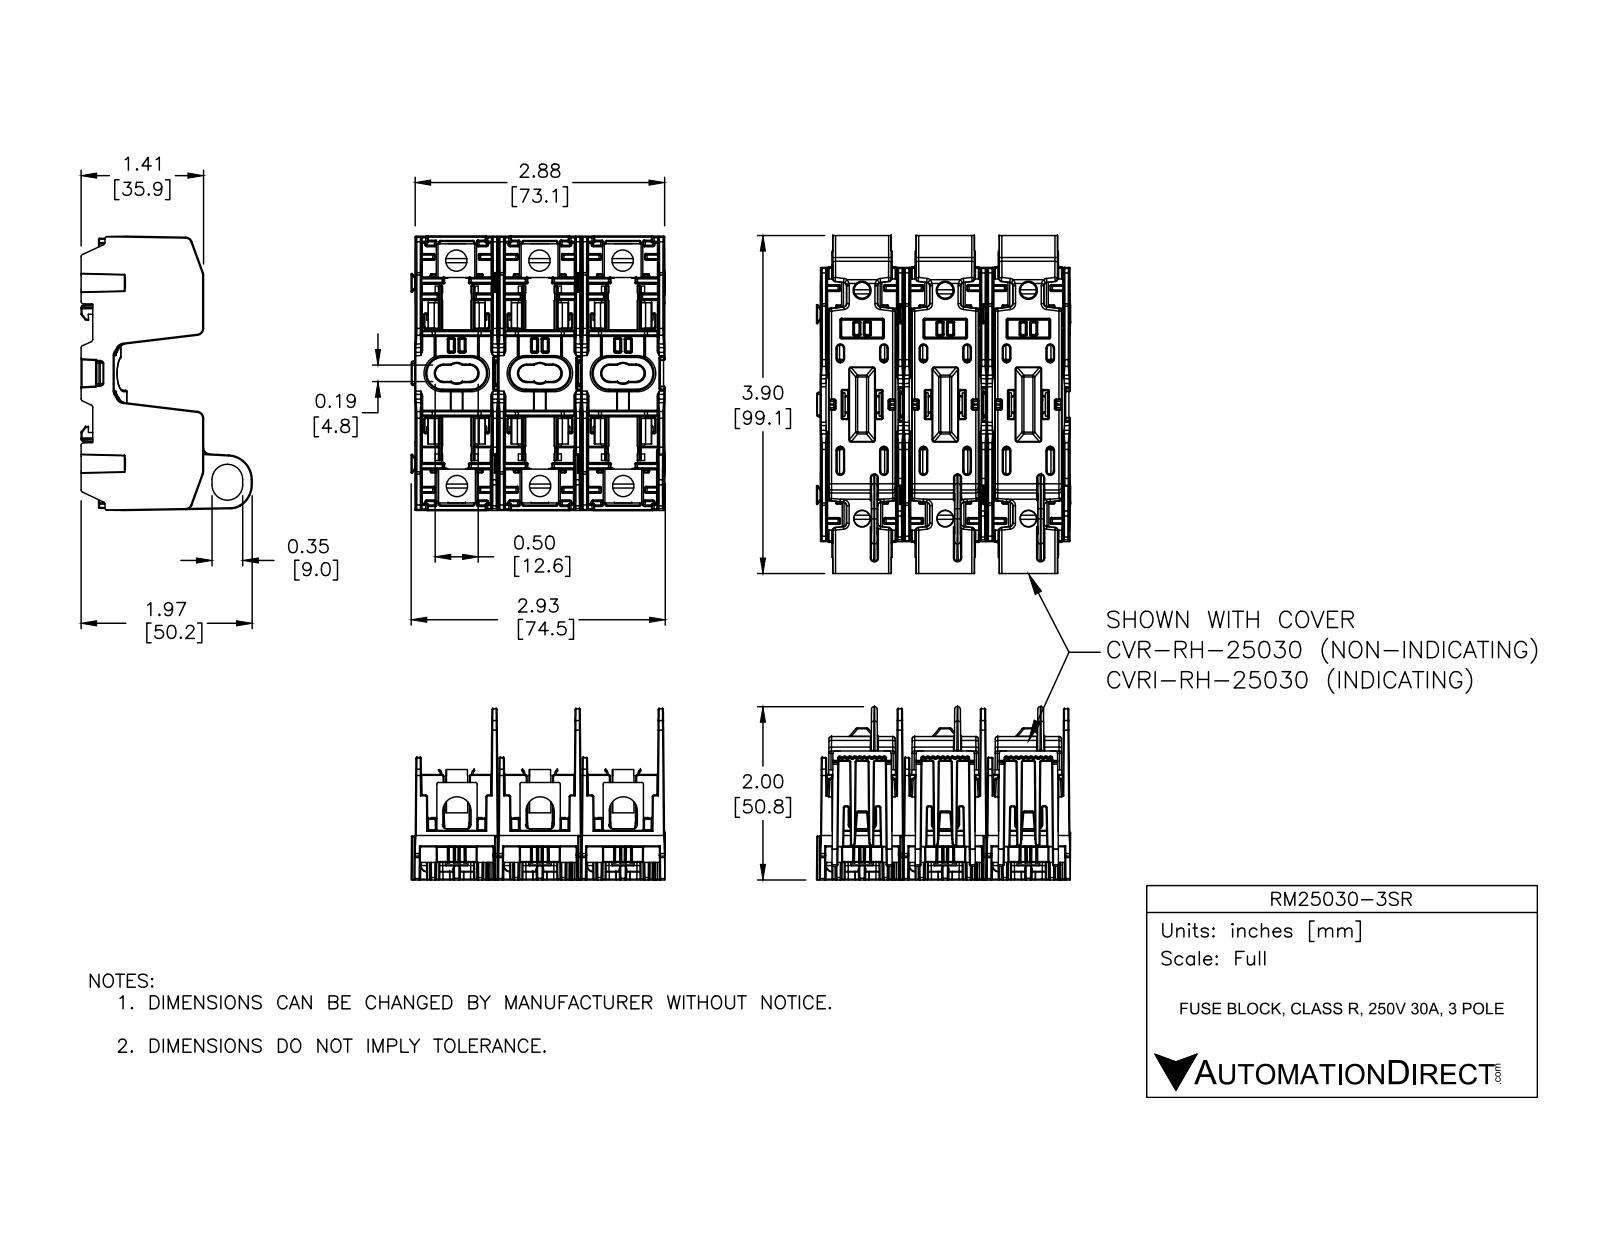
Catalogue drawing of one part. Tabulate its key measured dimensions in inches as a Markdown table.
| quantity | value |
| --- | --- |
| part name | RM25030-1SR; RM25030-3SR |
| STEP written by | SolidWorks 2016 (AUTOMOTIVE_DESIGN) |
| units | inches |
| bodies | 33 solids, 8703 faces (1950 planar, 3690 cylindrical, 3063 other) |
| overall size | 3.165 × 2.943 × 1.974 |
| volume | 4.261 in³ |
| surface area | 112.8 in² |
| round holes (diameter × count) | 0.142 × 6, 0.244 × 6 |
| round bosses / shafts (diameter × count) | 0.244 × 6 |
| partial cylindrical surfaces (radius × count) | 0.01 × 1140, 0.006 × 712, 0.02 × 197, 0.02 × 48, 0.079 × 37, 0.045 × 31, 0.03 × 23, 0.069 × 20 |
| main face-to-face distances | 0.965, 0.881, 0.965, 1.93, 1.93, 0.025, 0.083, 1.846, 0.344, 0.37 |
| hole center spacings | 0.965, 0.552, 2.048, 1.109, 1.115, 1.78, 1.93, 2.263 |
